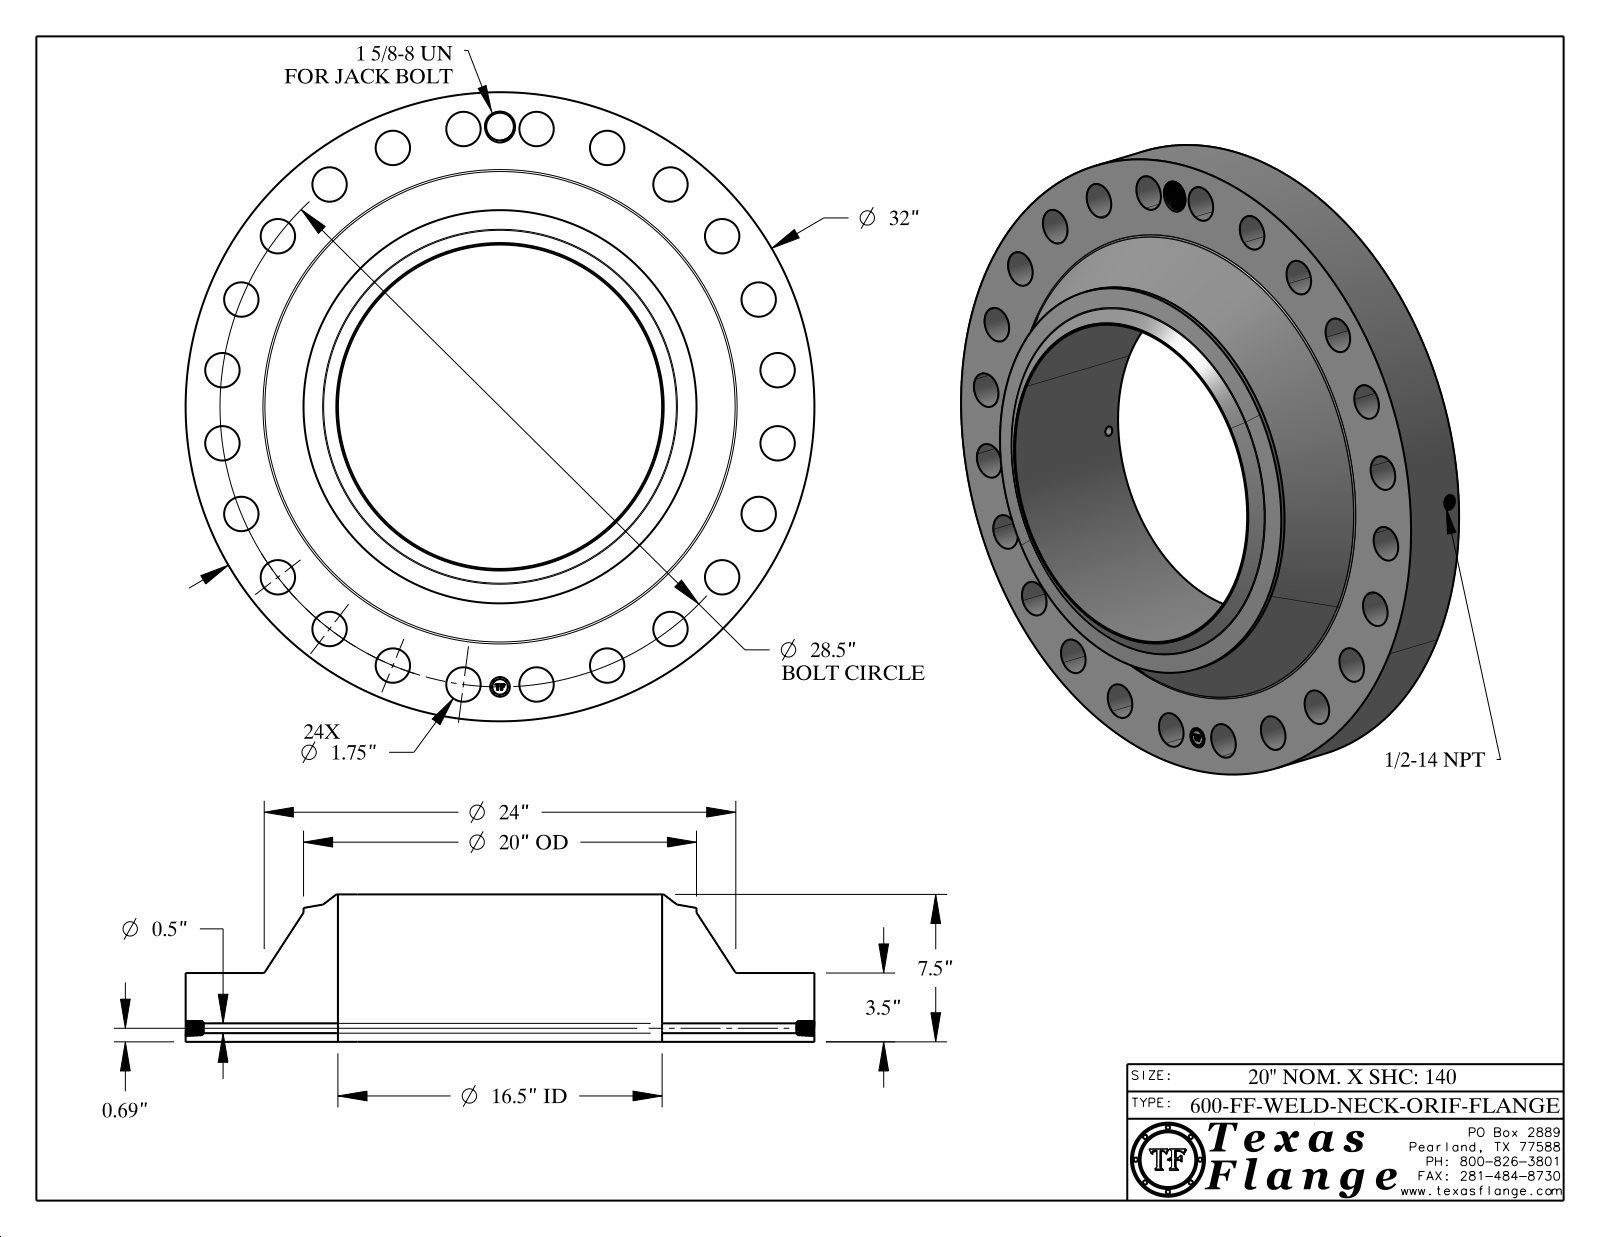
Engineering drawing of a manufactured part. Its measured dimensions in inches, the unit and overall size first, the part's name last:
Units: inches
Overall size (bounding box): 32 × 32 × 7.5
Round holes (diameter × count): ⌀1.75 ×24, ⌀0.5 ×1, ⌀0.672 ×1, ⌀1 ×1, ⌀1.409 ×1, ⌀16.5 ×1
Round bosses / shafts (diameter × count): ⌀0.061 ×8, ⌀32 ×1, ⌀20 ×1, ⌀0.788 ×1
Main face-to-face distances: 3.5, 7.5, 4, 3.485, 0.015, 4.015, 0.298, 0.293, 0.054, 0.248
Hole centre spacings: 14.25, 17.35, 24.681, 28.256, 10.906, 3.72, 7.376, 20.152
Volume: 2 416 in³ · Surface area: 2 465 in²
Bodies: 1 solid, 880 faces (368 planar, 149 cylindrical, 363 other)
Part name (STEP PRODUCT): 600-FF-WELD-NECK
STEP written by: CATIA V5 STEP AP214 (AUTOMOTIVE_DESIGN)
